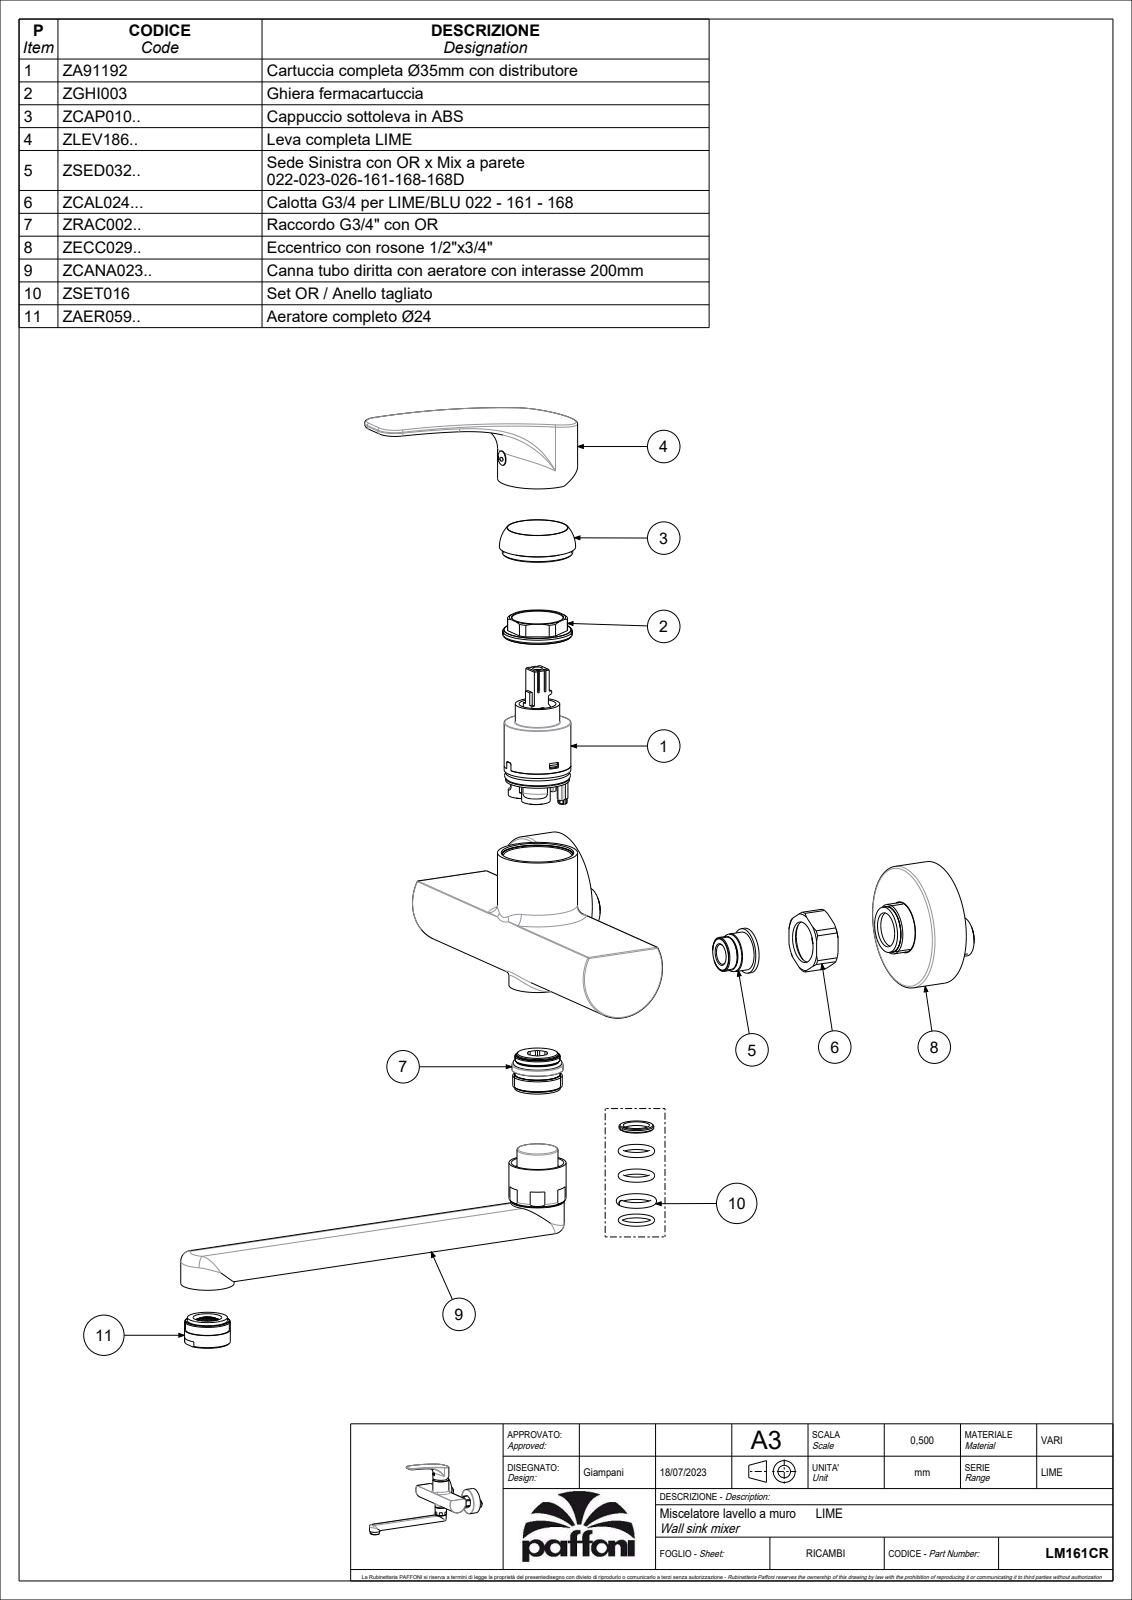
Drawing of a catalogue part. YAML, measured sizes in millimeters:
part_name: "LM161CR"
step_written_by: "CREO PARAMETRIC BY PTC INC, 2020044 (CONFIG_CONTROL_DESIGN)"
units: millimeters
bodies: {solids: 8, faces: 2655, planar: 1941, cylindrical: 421, other: 293}
overall_size: [272.6, 213.5, 165]
volume: 199374
surface_area: 187485
round_holes:
  - {diameter: 12, count: 5}
  - {diameter: 9, count: 3}
  - {diameter: 25, count: 3}
  - {diameter: 7, count: 2}
  - {diameter: 8, count: 2}
  - {diameter: 16.3, count: 2}
  - {diameter: 18, count: 2}
  - {diameter: 21.5, count: 2}
  - {diameter: 24.1, count: 2}
  - {diameter: 26, count: 2}
  - {diameter: 62.3, count: 2}
  - {diameter: 3, count: 1}
round_bosses_or_shafts:
  - {diameter: 24, count: 3}
  - {diameter: 63.5, count: 2}
  - {diameter: 42, count: 2}
  - {diameter: 28, count: 2}
  - {diameter: 27, count: 2}
  - {diameter: 23.8, count: 2}
  - {diameter: 20.8, count: 2}
  - {diameter: 10, count: 2}
partial_cylinders:
  - {radius: 0.5, count: 66}
  - {radius: 0.3, count: 20}
  - {radius: 1, count: 18}
  - {radius: 5.25, count: 3}
  - {radius: 7, count: 3}
  - {radius: 7.25, count: 3}
  - {radius: 0.2, count: 2}
  - {radius: 1.2, count: 2}
face_to_face_distances: [2.5, 0.6, 1, 15, 67.5, 110, 59.92, 14, 74.92, 77.42]
hole_center_spacings: [0.71, 8.51, 8.6, 13.04, 13.21, 13.51, 98.6, 194.61]
